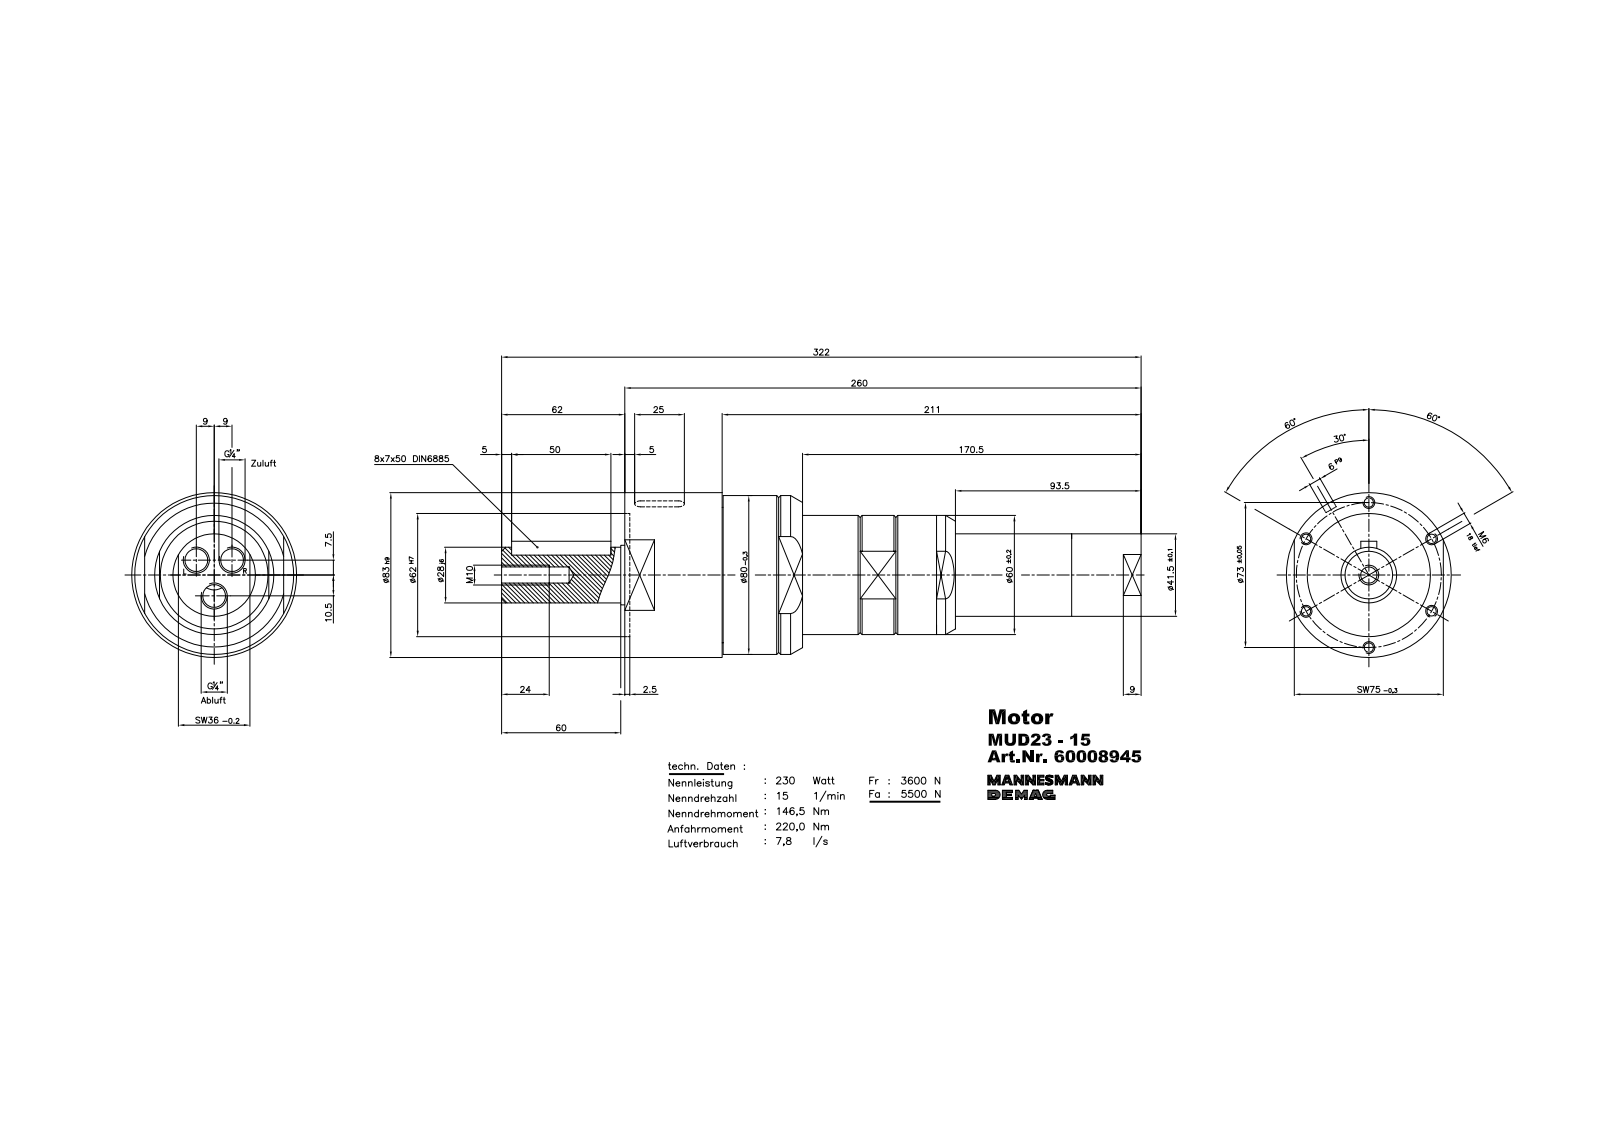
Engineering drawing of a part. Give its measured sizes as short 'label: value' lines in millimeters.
name: MUD 23-15_60008945
written by: Autodesk Inventor 2008 (CONFIG_CONTROL_DESIGN)
unit: mm
bodies: 1 solid, 237 faces (123 planar, 49 cylindrical, 65 other)
size: 322 × 83 × 83
volume: 820 579 mm³; area: 75 653 mm²
holes: 2× ⌀1.55, 2× ⌀4, 2× ⌀5.5, 1× ⌀38, 1× ⌀42, 1× ⌀58.69, 1× ⌀62
bosses: 2× ⌀5, 2× ⌀3.6, 1× ⌀83, 1× ⌀80, 1× ⌀73.36, 1× ⌀60, 1× ⌀45, 1× ⌀41.5
rounds: 2× R2.25, 2× R3, 2× R4, 2× R5, 2× R32.5, 1× R7.5, 1× R17.5, 1× R27
face distances: 3.59, 89.5, 85.91, 0.5, 49, 45.41, 40.5, 77, 260, 256.41
